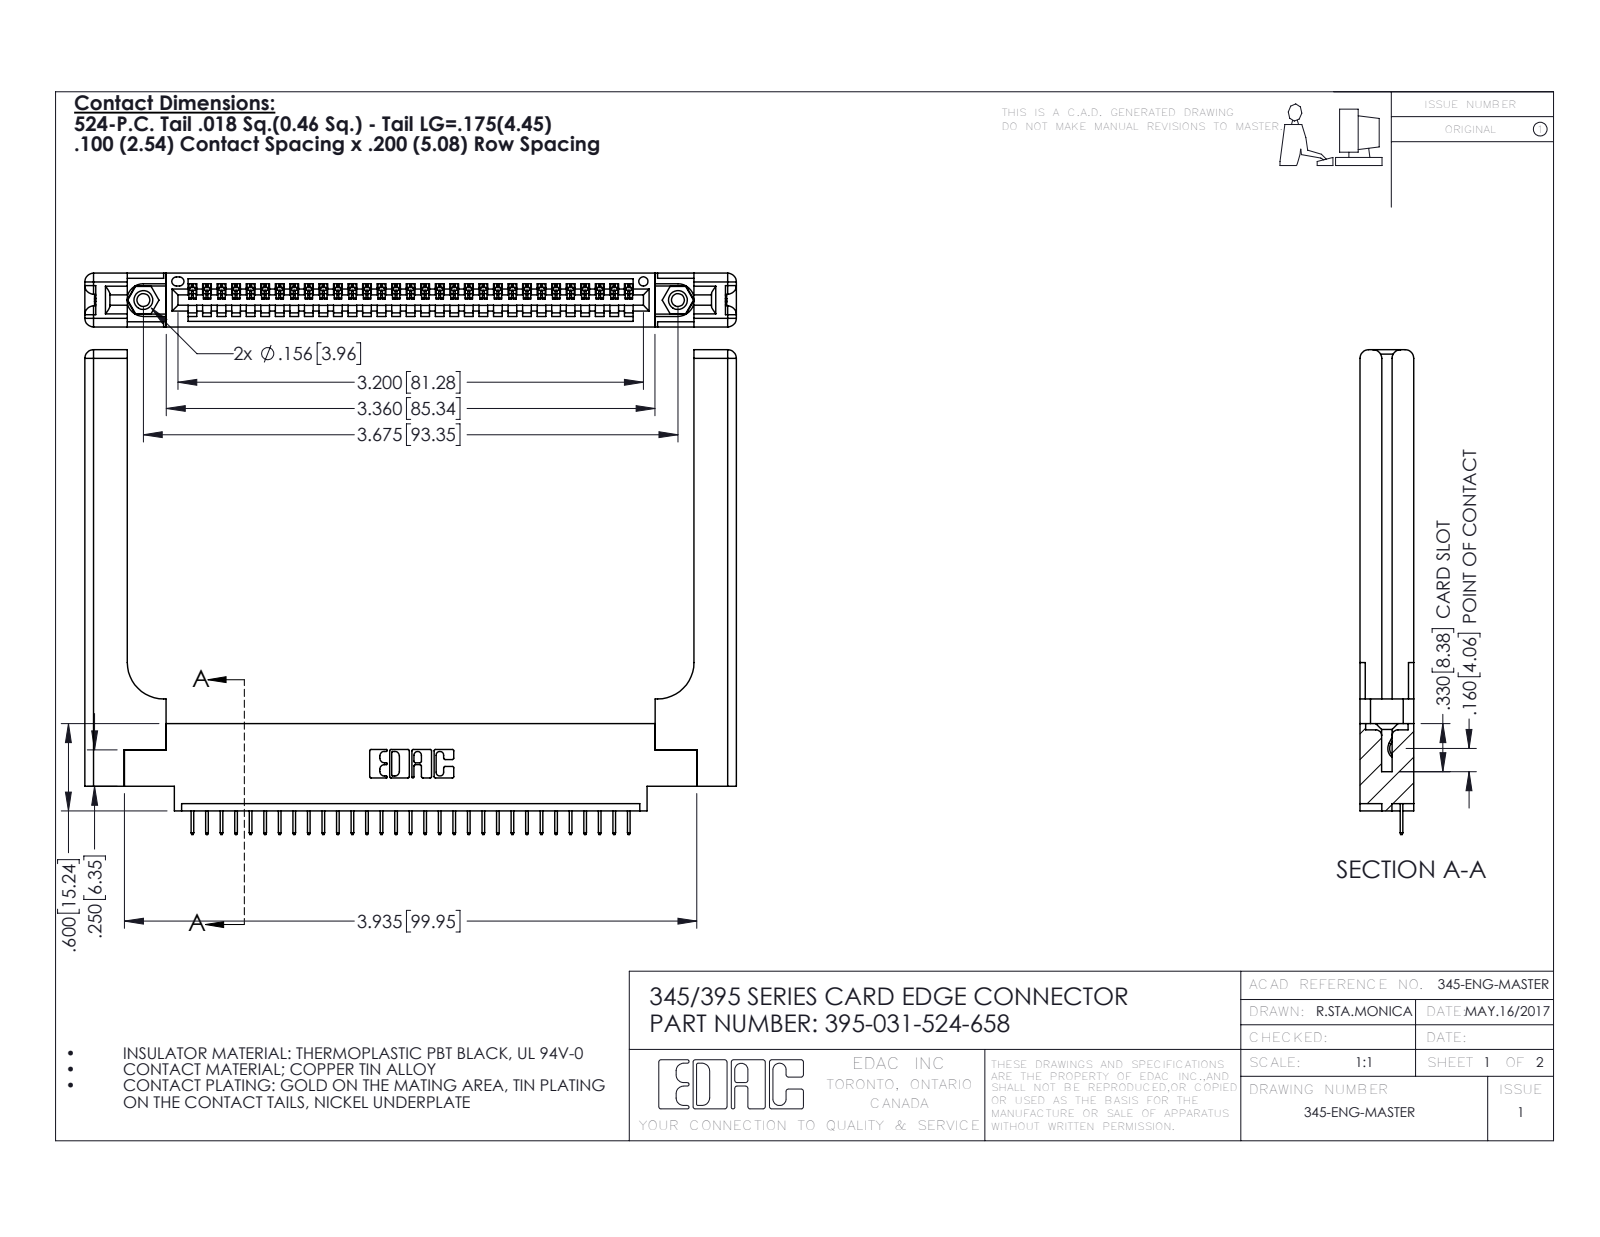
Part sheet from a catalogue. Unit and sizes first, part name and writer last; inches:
Units: inches
Overall size (bounding box): 4.479 × 3.332 × 0.37
Round holes (diameter × count): ⌀0.089 ×2, ⌀0.125 ×2, ⌀0.156 ×2, ⌀0.064 ×1
Round bosses / shafts (diameter × count): ⌀0.155 ×2
Partial cylindrical surfaces — rounded edges, fillets, slot ends (radius × count): R0.006 ×62, R0.01 ×22, R0.06 ×16, R0.007 ×6, R0.031 ×6, R0.026 ×3, R0.03 ×2, R0.031 ×2
Main face-to-face distances: 0.37, 0.072, 0.298, 0.148, 0.15, 0.098, 0.272, 0.025, 0.2, 0.077
Hole centre spacings: 0.27, 3.44, 3.675
Volume: 1.159 in³ · Surface area: 29.17 in²
Bodies: 36 solids, 2308 faces (1658 planar, 590 cylindrical, 60 other)
Part name (STEP PRODUCT): 345 Part_0.170 Offset - 0.156 Dia-TH; 345-250-001_345-250-001-102; 345-292-001_345-293-124; 395-031-524-658 (+1 more)
STEP written by: SolidWorks 2016 (CONFIG_CONTROL_DESIGN)
